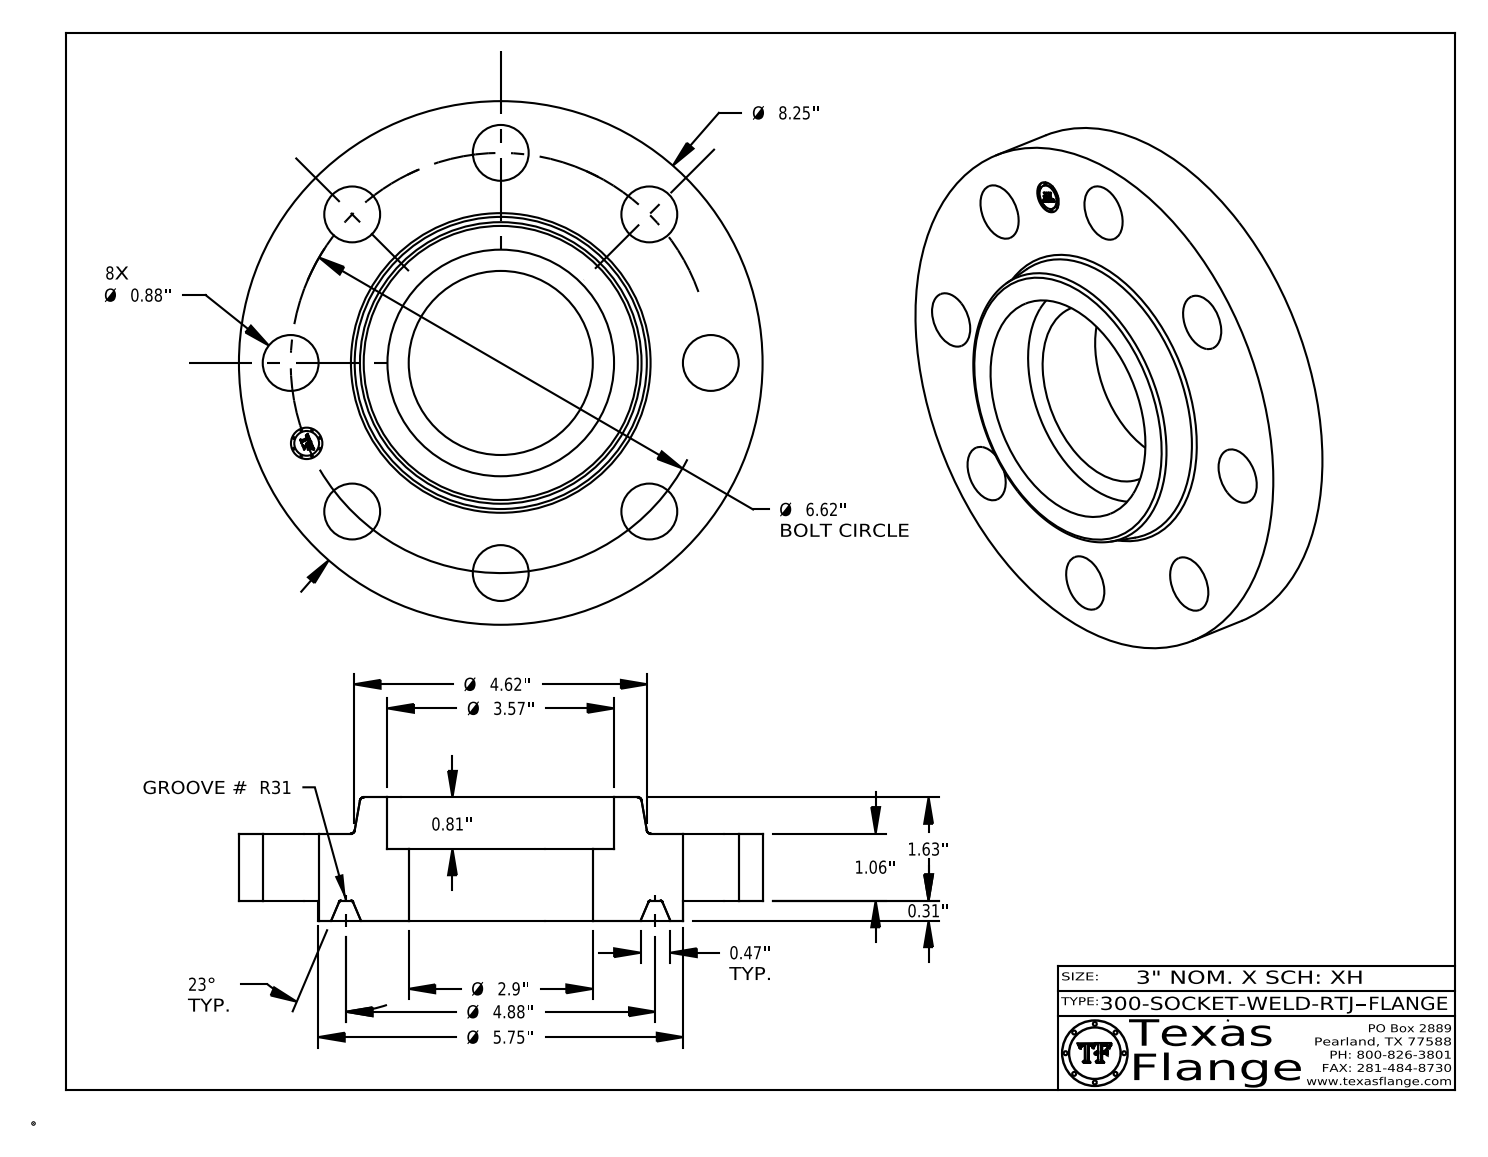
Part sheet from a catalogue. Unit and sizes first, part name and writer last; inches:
Units: inches
Overall size (bounding box): 8.25 × 8.25 × 1.943
Round holes (diameter × count): ⌀0.88 ×8, ⌀0.495 ×1, ⌀2.9 ×1, ⌀3.57 ×1
Round bosses / shafts (diameter × count): ⌀0.03 ×8, ⌀8.25 ×1, ⌀5.75 ×1, ⌀0.39 ×1
Main face-to-face distances: 1.06, 0.313, 1.373, 1.943, 1.63, 0.57, 1.133, 0.82, 0.24, 0.81
Hole centre spacings: 3.31, 2.533, 6.116, 4.681, 4.681, 1.291, 3.678, 6.493
Volume: 51.58 in³ · Surface area: 172.6 in²
Bodies: 1 solid, 438 faces (372 planar, 52 cylindrical, 14 other)
Part name (STEP PRODUCT): 300-SOCKET-WELD-RTJ
STEP written by: CATIA V5 STEP AP214 (AUTOMOTIVE_DESIGN)
